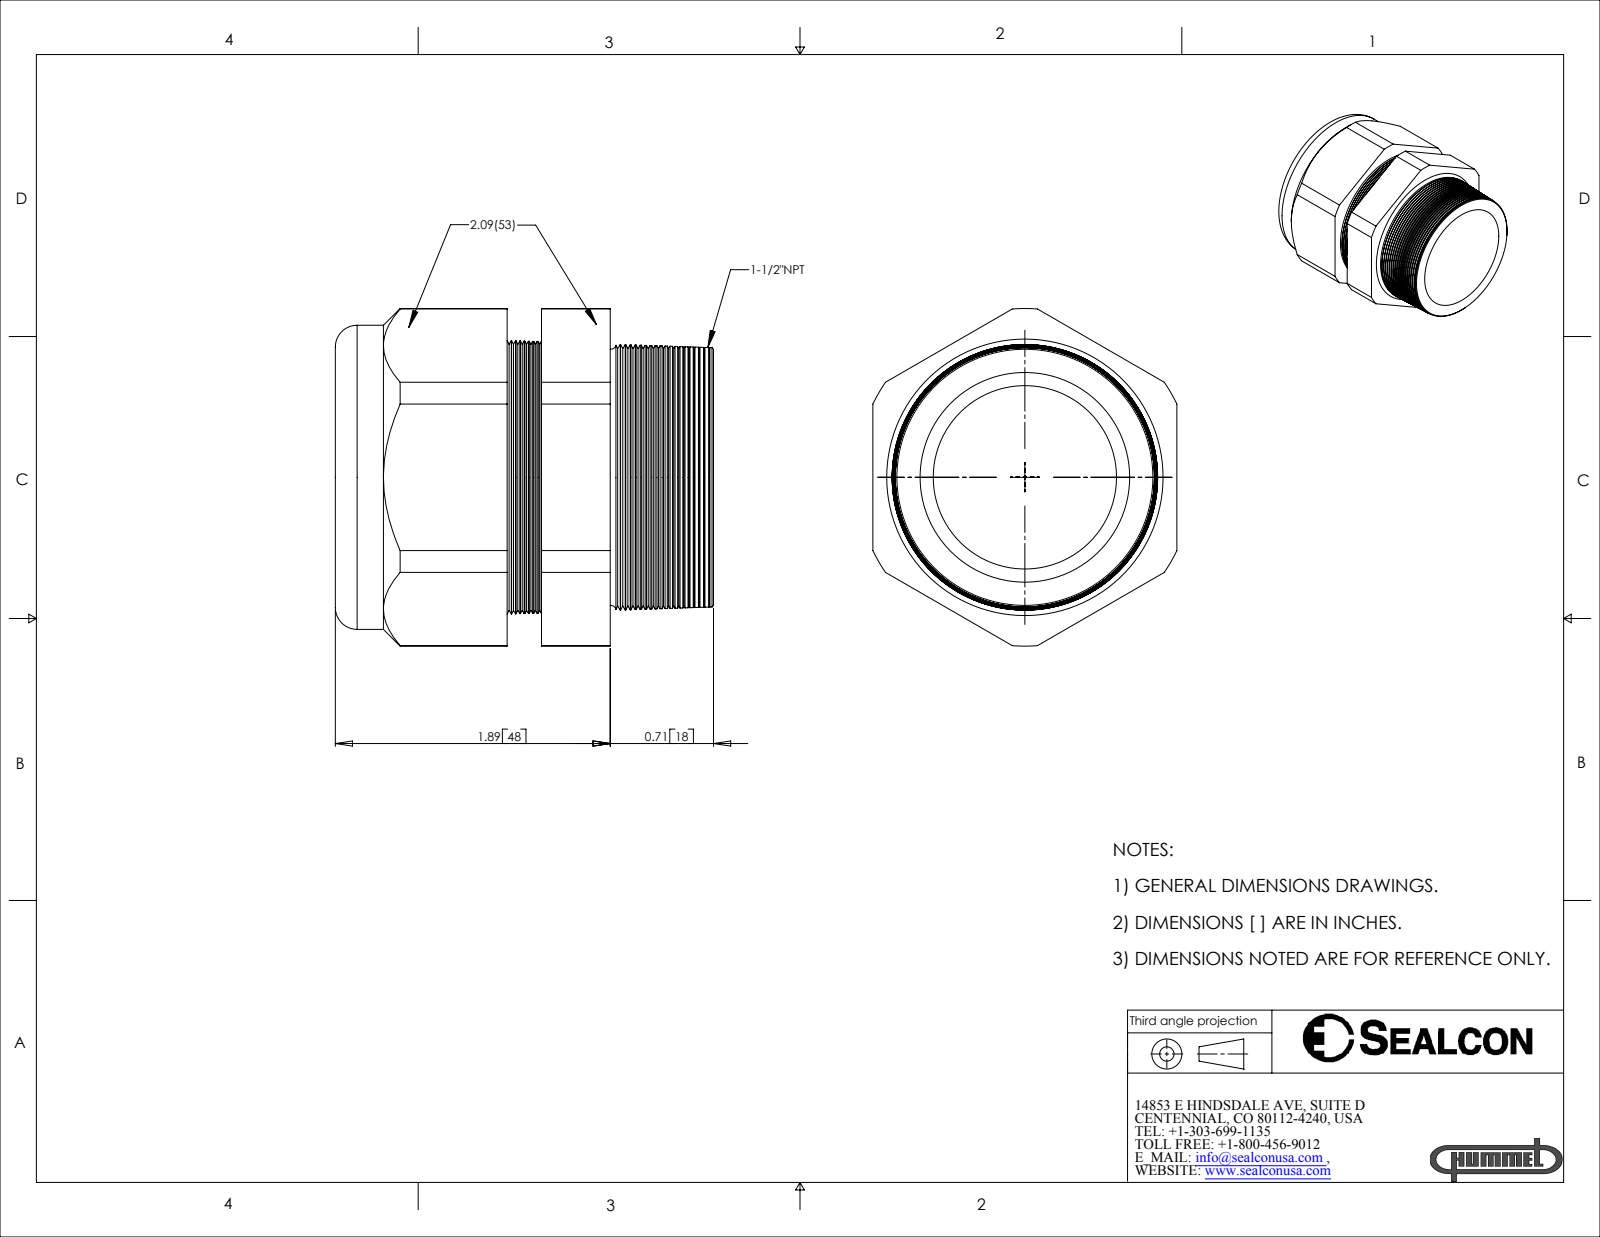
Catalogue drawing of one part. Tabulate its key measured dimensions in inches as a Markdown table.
| quantity | value |
| --- | --- |
| part name | CD36NP-GY |
| STEP written by | SolidWorks 2007 (CONFIG_CONTROL_DESIGN) |
| units | inches |
| bodies | 2 solids, 235 faces (21 planar, 20 cylindrical, 194 other) |
| overall size | 2.68 × 2.32 × 2.09 |
| volume | 5.665 in³ |
| surface area | 42.62 in² |
| round holes (diameter × count) | 1.24 × 1, 1.26 × 1 |
| round bosses / shafts (diameter × count) | 2.09 × 1 |
| partial cylindrical surfaces (radius × count) | 1.16 × 1 |
| main face-to-face distances | 2.09, 0.5, 0.02, 0.48, 1.418, 1.398, 0.918, 1.181, 1.161, 0.681 |
